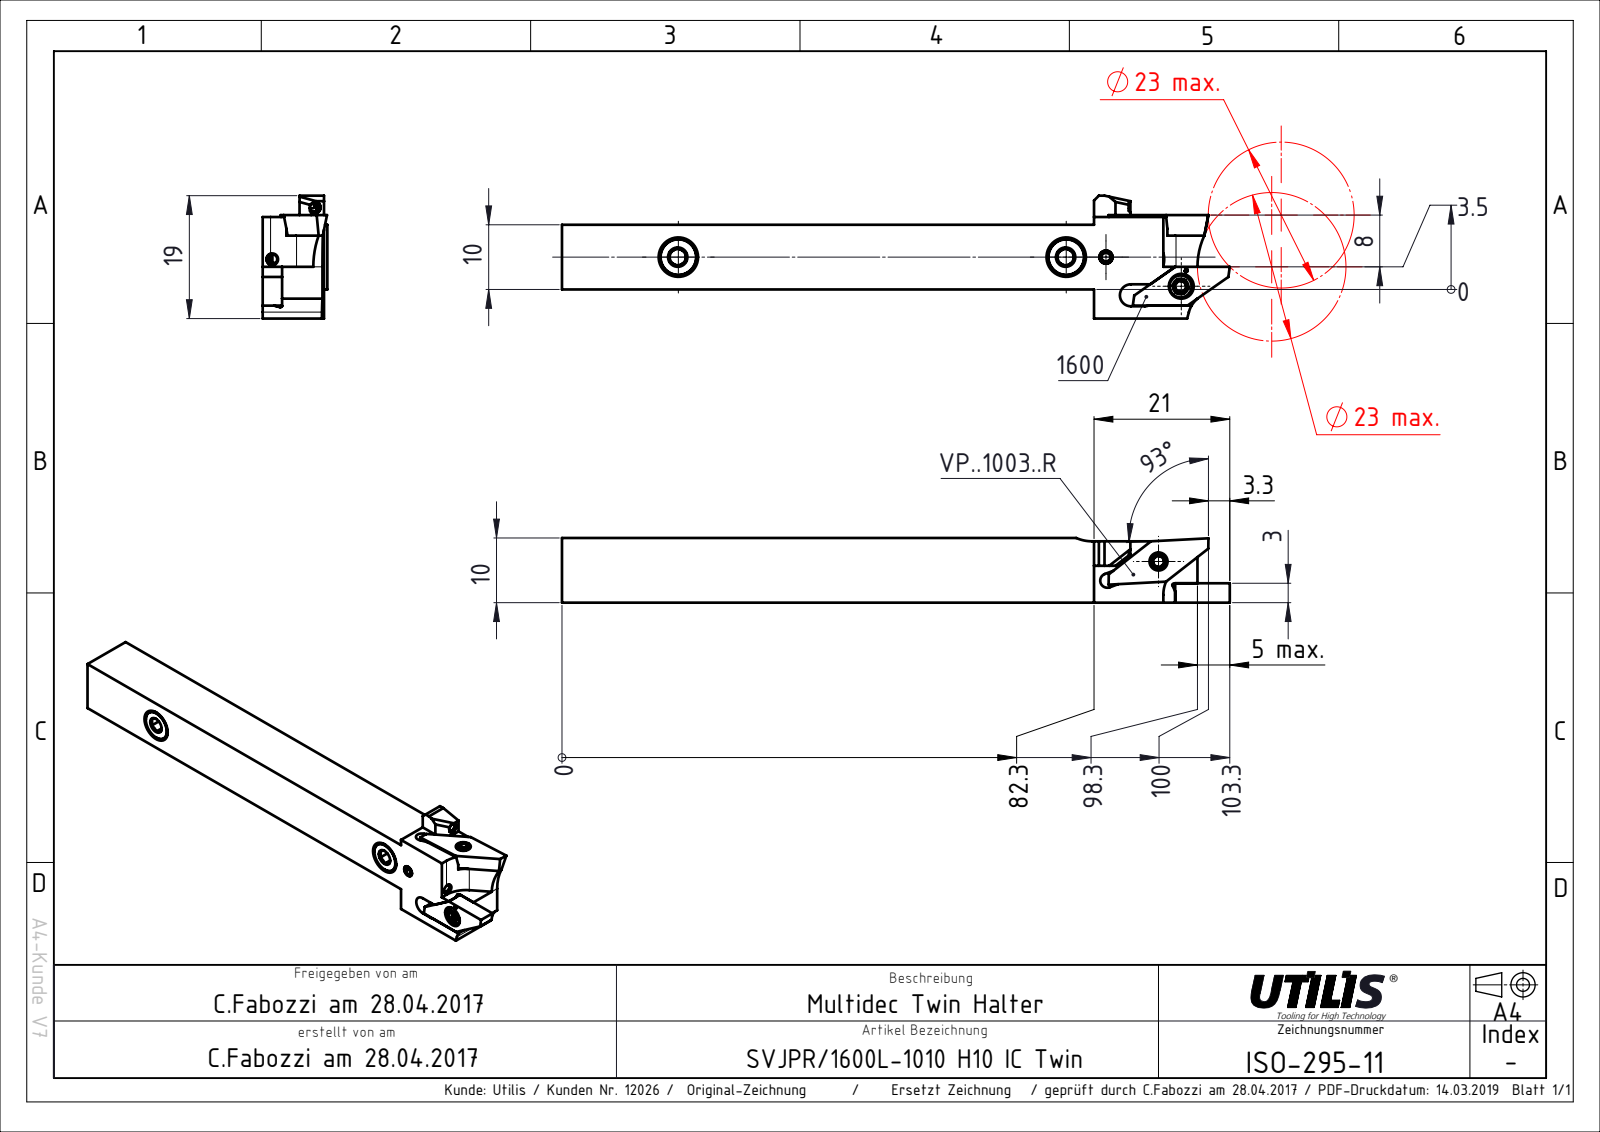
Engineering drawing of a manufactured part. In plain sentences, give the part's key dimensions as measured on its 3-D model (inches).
The part is named "ISO-295-11". Its 3-D file was written by "SolidWorks 2016 (AUTOMOTIVE_DESIGN)". It is 1 solid with 81 faces: 67 planar, 12 cylindrical and 2 other. Overall it measures 4.067 by 0.748 by 0.394 inches. Its volume is 0.638 cubic inches and its surface area 7.223 square inches. Partial cylindrical surfaces (rounded edges, fillets, slot ends): 2 of radius 0.01, 2 of radius 0.24, 1 of radius 0.02, 1 of radius 0.043, 1 of radius 0.061, 1 of radius 0.067, 1 of radius 0.161, 1 of radius 0.201. The main face-to-face distances are 0.394, 0.177, 0.571, 0.63, 0.315, 3.24, 0.453, 0.059, 0.375, 0.019.
